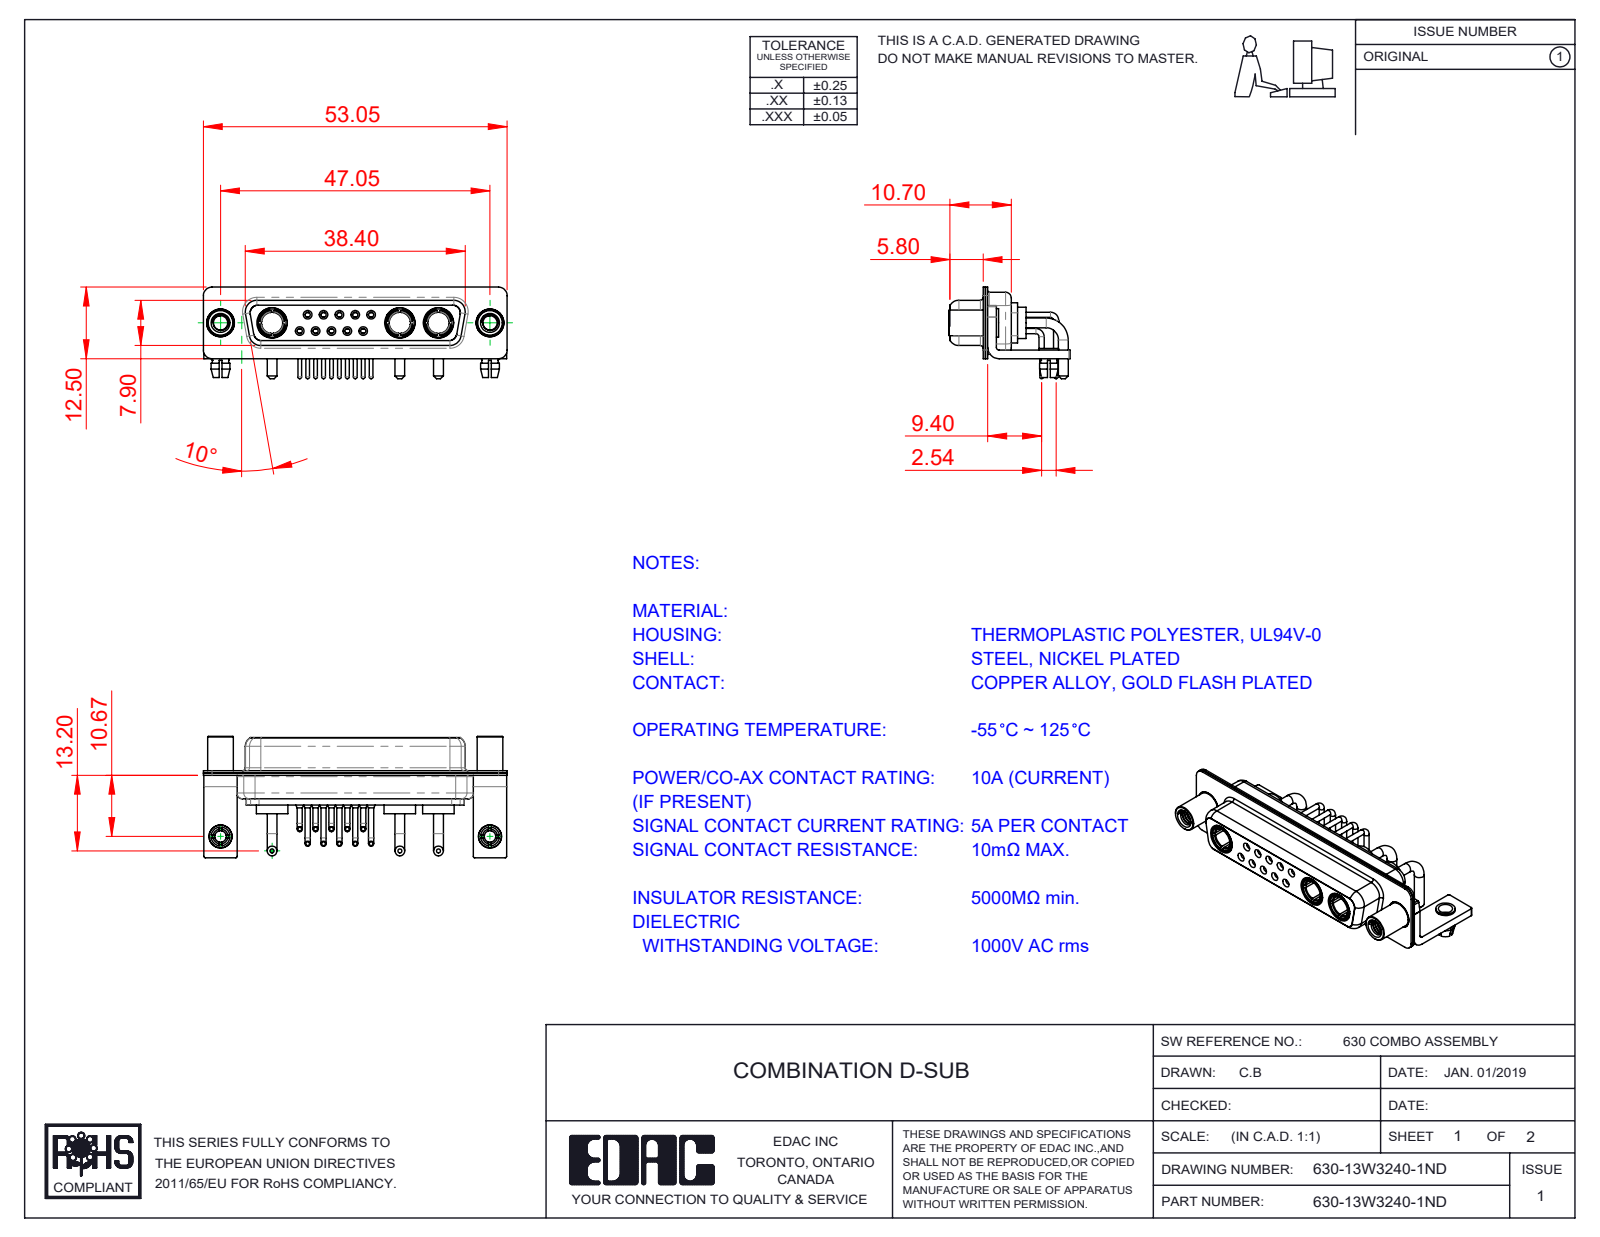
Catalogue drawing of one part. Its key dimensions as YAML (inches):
part_name: "630Combo Shell Front_25 Contacts; 630Combo Stabilizer Bracket; 630Combo Contact Row 2; 630Combo Contact Row 1 (+6 more)"
step_written_by: "SolidWorks 2020 (CONFIG_CONTROL_DESIGN)"
units: inches
bodies: {solids: 25, faces: 1233, planar: 374, cylindrical: 546, other: 313}
overall_size: [2.089, 0.835, 0.63]
volume: 0.261
surface_area: 15.5
round_holes:
  - {diameter: 0.079, count: 12}
  - {diameter: 0.035, count: 10}
  - {diameter: 0.043, count: 10}
  - {diameter: 0.059, count: 10}
  - {diameter: 0.063, count: 5}
  - {diameter: 0.067, count: 5}
  - {diameter: 0.191, count: 5}
  - {diameter: 0.098, count: 4}
  - {diameter: 0.146, count: 3}
  - {diameter: 0.209, count: 3}
  - {diameter: 0.126, count: 2}
  - {diameter: 0.157, count: 2}
round_bosses_or_shafts:
  - {diameter: 0.035, count: 10}
  - {diameter: 0.026, count: 10}
  - {diameter: 0.067, count: 6}
  - {diameter: 0.063, count: 5}
  - {diameter: 0.217, count: 3}
  - {diameter: 0.205, count: 3}
  - {diameter: 0.195, count: 3}
  - {diameter: 0.187, count: 3}
partial_cylinders:
  - {radius: 0.01, count: 16}
  - {radius: 0.059, count: 16}
  - {radius: 0.079, count: 13}
  - {radius: 0.053, count: 8}
  - {radius: 0.063, count: 8}
  - {radius: 0.02, count: 5}
  - {radius: 0.024, count: 4}
  - {radius: 0.026, count: 4}
face_to_face_distances: [0.016, 0.018, 0.055, 0.333, 0.071, 0.35, 0.031, 0.059, 0.244, 0.278]
hole_center_spacings: [0.124, 0.109, 0.218, 0.198, 0.198, 0.327, 0.294, 0.295]
